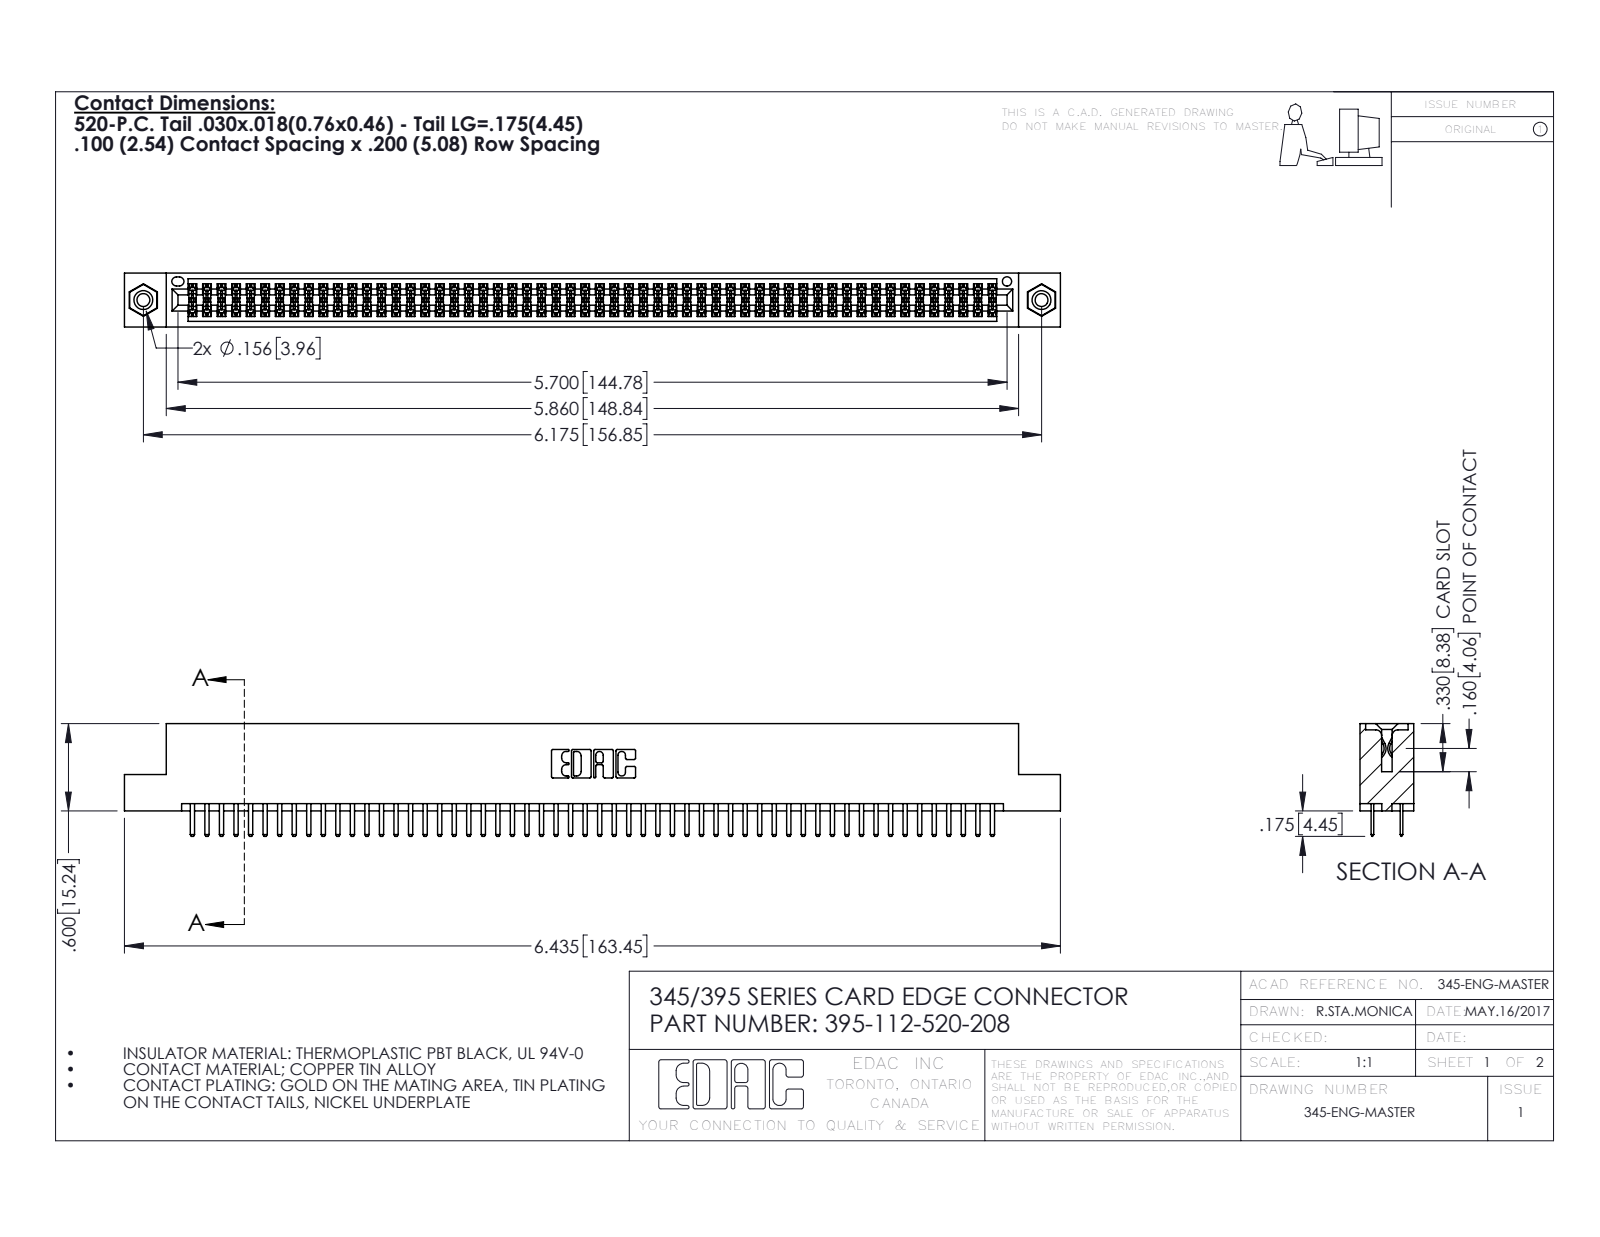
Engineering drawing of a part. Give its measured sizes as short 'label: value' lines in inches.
name: 345 Part_Flush Mounting Lugs - 0.156 Dia-TI; 395-112-520-208; 345-250-001_345-250-003-102; 345-292-001_345-293-120
written by: SolidWorks 2016 (CONFIG_CONTROL_DESIGN)
unit: in
bodies: 115 solids, 6234 faces (4032 planar, 2186 cylindrical, 16 other)
size: 6.435 × 0.775 × 0.37
volume: 0.973 in³; area: 36.83 in²
holes: 2× ⌀0.089, 2× ⌀0.125, 2× ⌀0.156, 1× ⌀0.064
bosses: 2× ⌀0.155
rounds: 168× R0.006, 116× R0.01, 22× R0.01, 6× R0.007, 6× R0.031, 3× R0.026, 2× R0.014, 2× R0.019
face distances: 0.072, 0.298, 0.2, 0.37, 0.098, 0.272, 0.025, 0.225, 0.022, 0.072
hole spacings: 0.27, 5.939, 6.175
